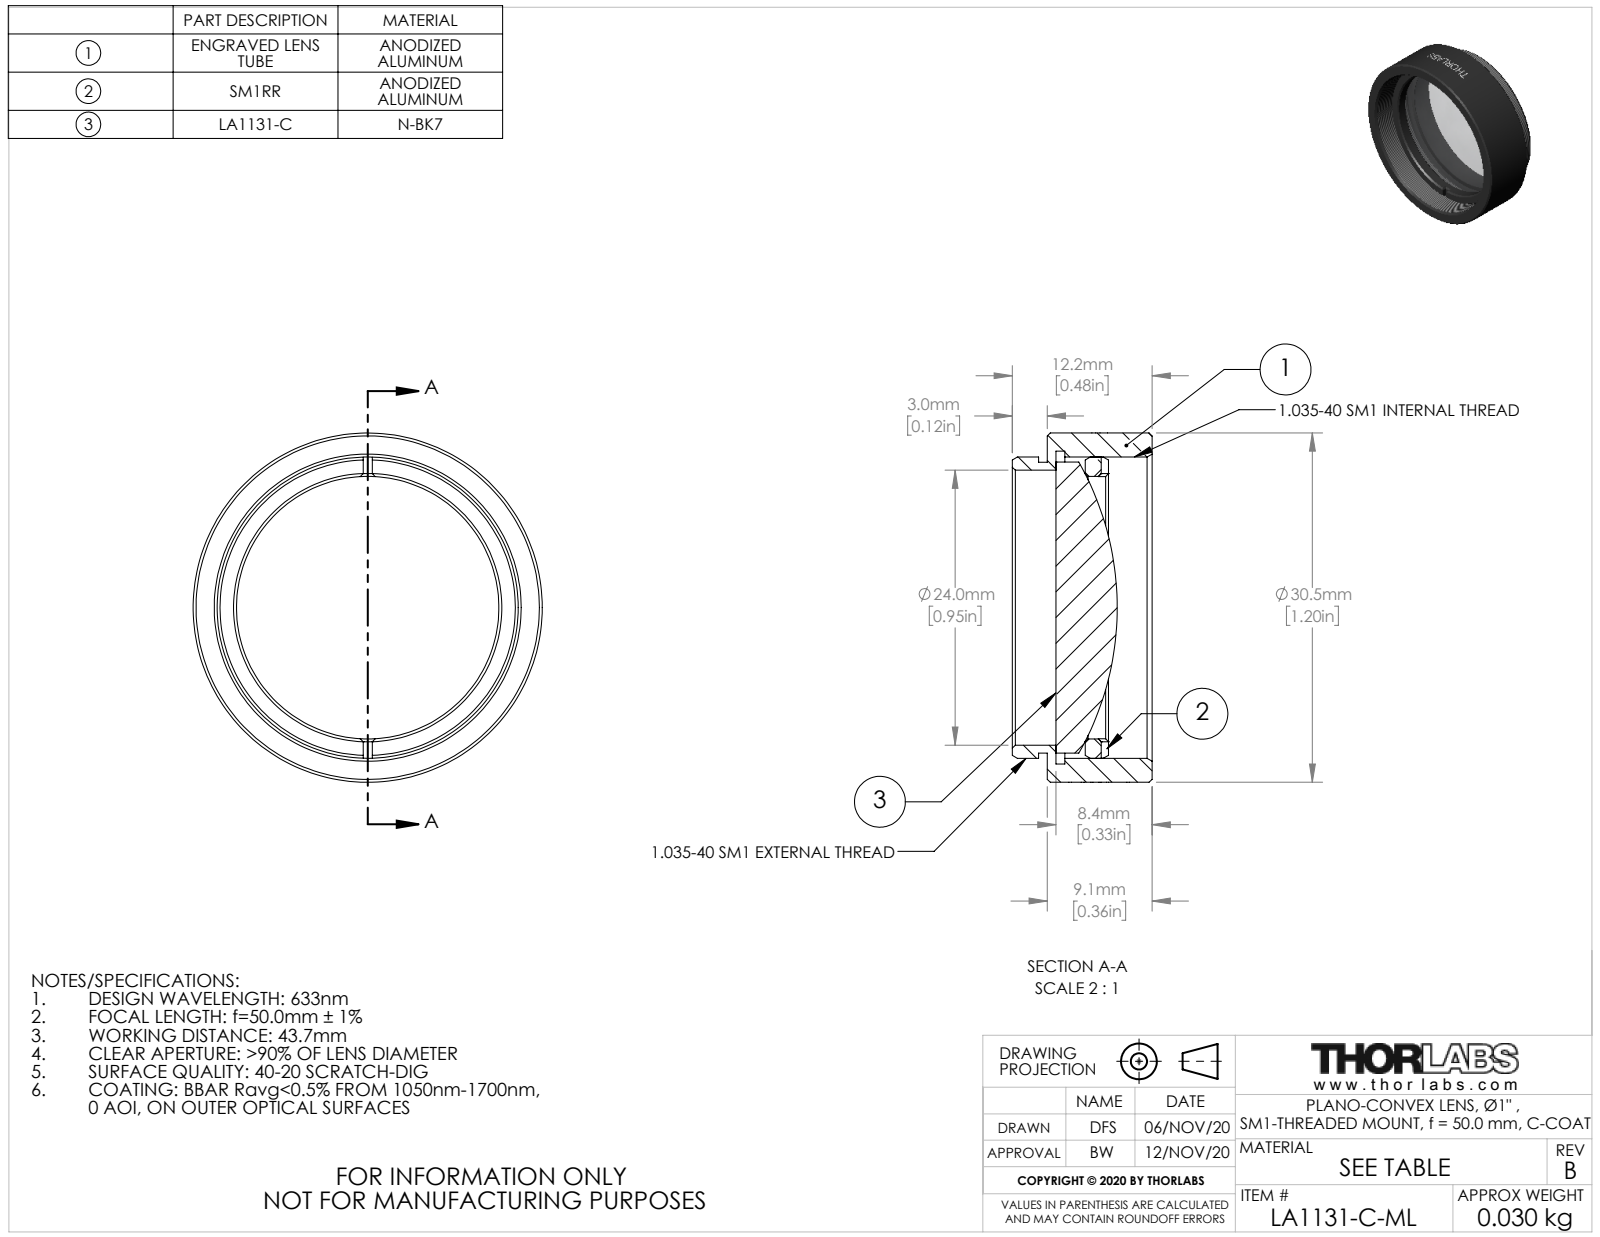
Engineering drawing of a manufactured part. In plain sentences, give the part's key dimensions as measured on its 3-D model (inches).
The part is named "24421-E0W". Its 3-D file was written by "SolidWorks 2018 (CONFIG_CONTROL_DESIGN)". It is 3 solids with 148 faces: 20 planar, 104 cylindrical and 24 other. Overall it measures 1.2 by 1.2 by 0.48 inches. Its volume is 0.25 cubic inches and its surface area 6.949 square inches. Round holes: 1 of diameter 0.902, 1 of diameter 0.945, 1 of diameter 1.035, 1 of diameter 1.075. Round bosses or shafts: 1 of diameter 1.2, 1 of diameter 1.035, 1 of diameter 1, 1 of diameter 0.999. The main face-to-face distances are 0.03, 0.36, 0.33, 0.13, 0.1, 0.23, 0.211, 0.181, 0.08, 0.15.
